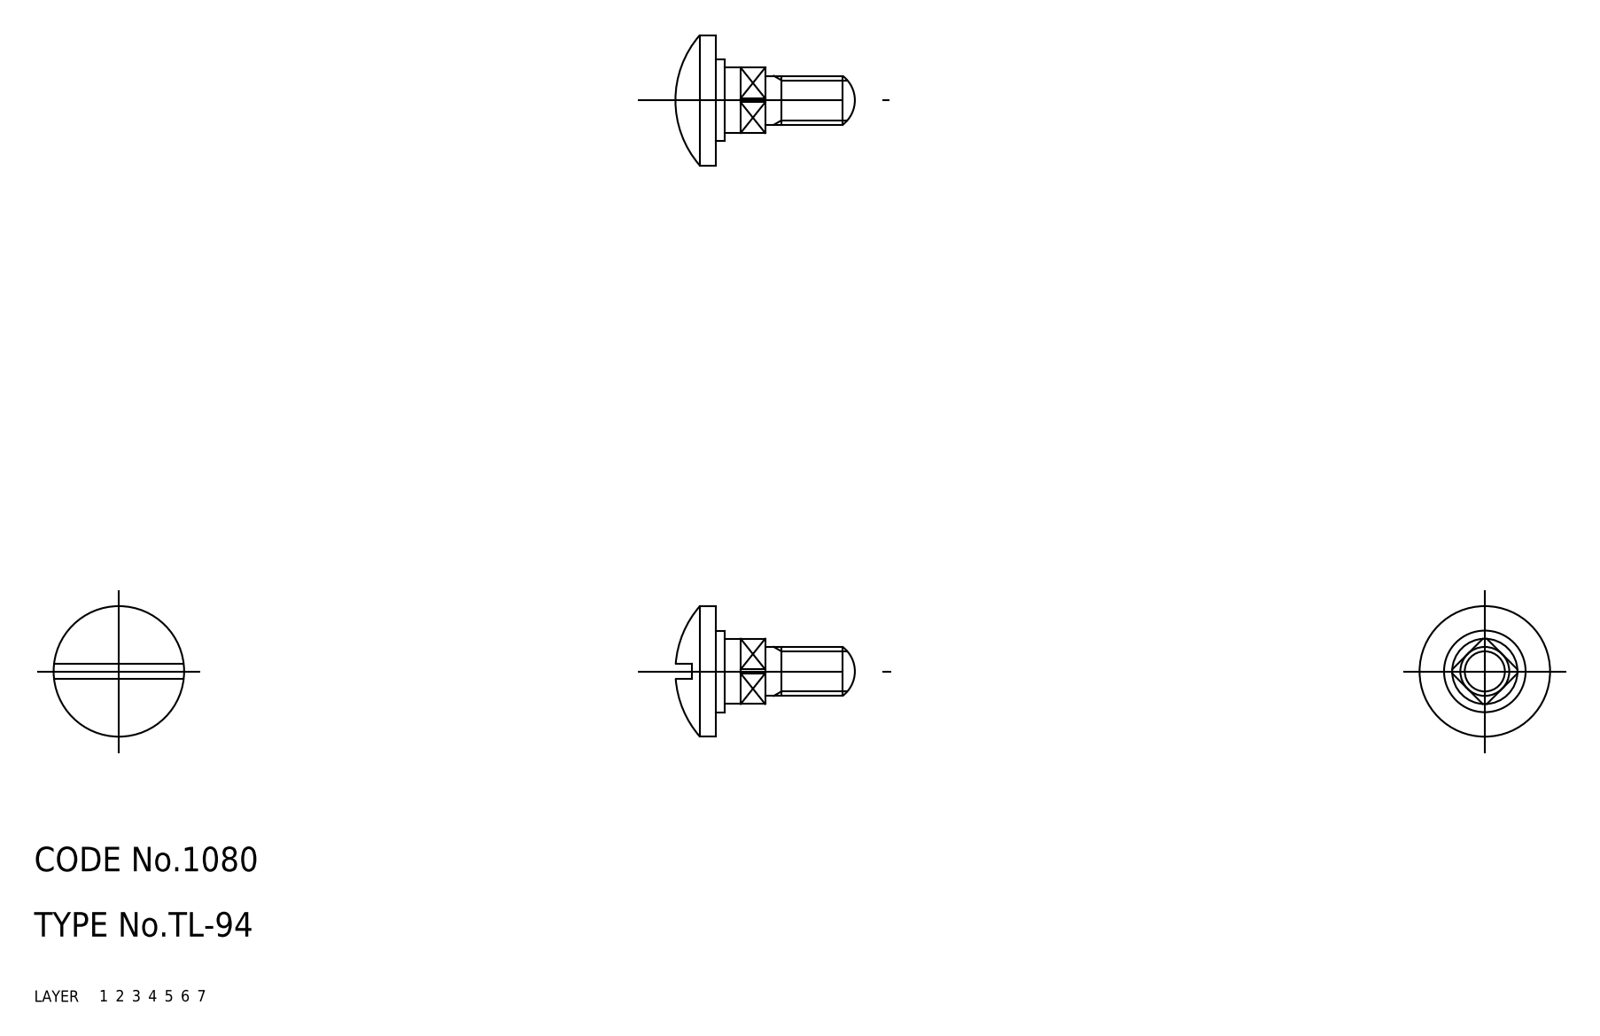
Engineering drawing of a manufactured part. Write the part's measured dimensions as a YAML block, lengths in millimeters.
part_name: "knob"
step_written_by: "CADfix (AUTOMOTIVE_DESIGN)"
units: millimeters
bodies: {solids: 1, faces: 27, planar: 0, cylindrical: 0, other: 27}
overall_size: [21.97, 16, 16]
volume: 1265
surface_area: 903
